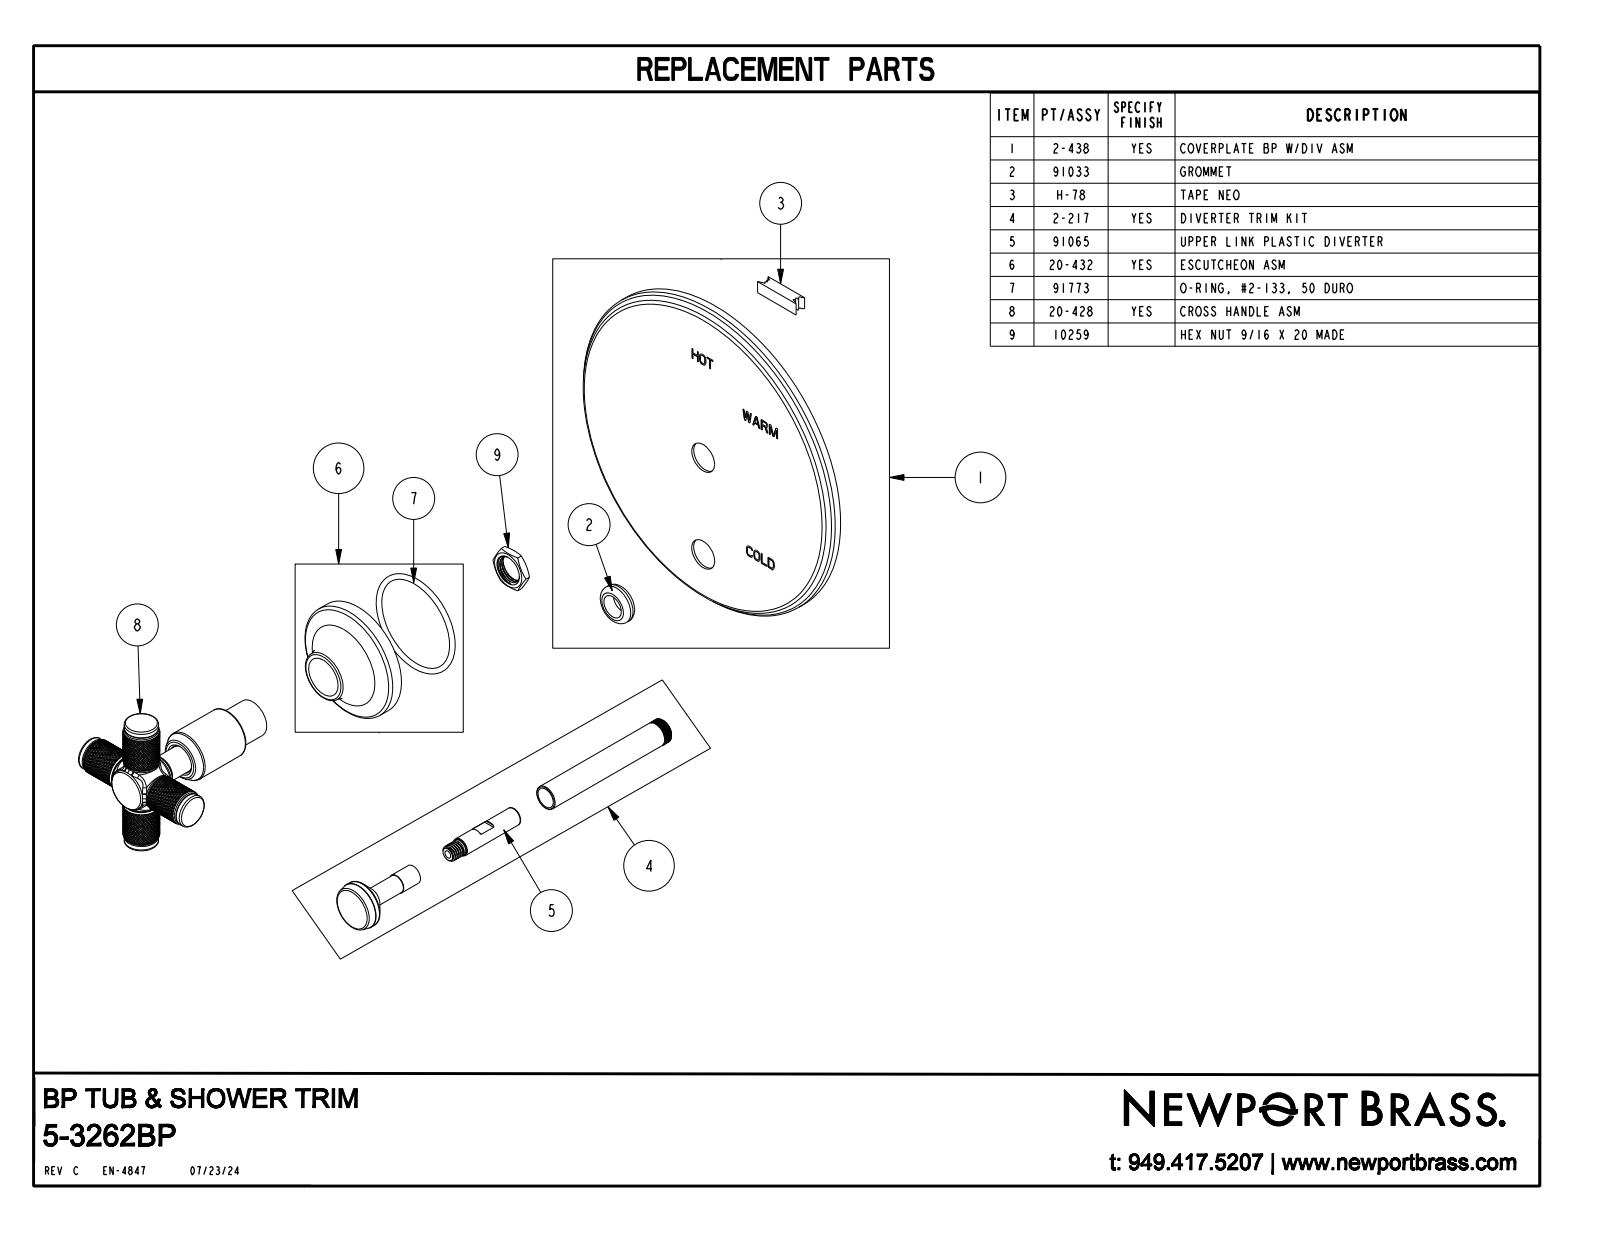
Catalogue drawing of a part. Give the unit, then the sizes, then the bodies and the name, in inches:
Units: inches
Overall size (bounding box): 6.504 × 6.5 × 6.5
Round holes (diameter × count): ⌀0.25 ×2, ⌀0.403 ×2, ⌀0.47 ×2, ⌀0.11 ×1, ⌀0.14 ×1, ⌀0.15 ×1, ⌀0.265 ×1, ⌀0.275 ×1, ⌀0.318 ×1, ⌀0.345 ×1, ⌀0.358 ×1, ⌀0.36 ×1
Round bosses / shafts (diameter × count): ⌀0.67 ×2, ⌀0.63 ×2, ⌀0.433 ×2, ⌀0.37 ×2, ⌀6.5 ×1, ⌀2.25 ×1, ⌀1.812 ×1, ⌀0.965 ×1
Partial cylindrical surfaces — rounded edges, fillets, slot ends (radius × count): R0.01 ×6, R0.042 ×6, R0.072 ×1, R0.137 ×1, R0.149 ×1, R0.169 ×1, R0.394 ×1
Main face-to-face distances: 0.05, 0.25, 0.3, 0.465, 0.263, 0.313, 0.563, 1.565, 1.302, 1.252
Hole centre spacings: 2.17
Volume: 5.771 in³ · Surface area: 328.6 in²
Bodies: 22 solids, 12211 faces (528 planar, 2726 cylindrical, 8957 other)
Part name (STEP PRODUCT): 11118_AF3; 91033; H-78; 2-438_AF3_ASM (+8 more)
STEP written by: CREO PARAMETRIC BY PTC INC, 2018400 (CONFIG_CONTROL_DESIGN)
